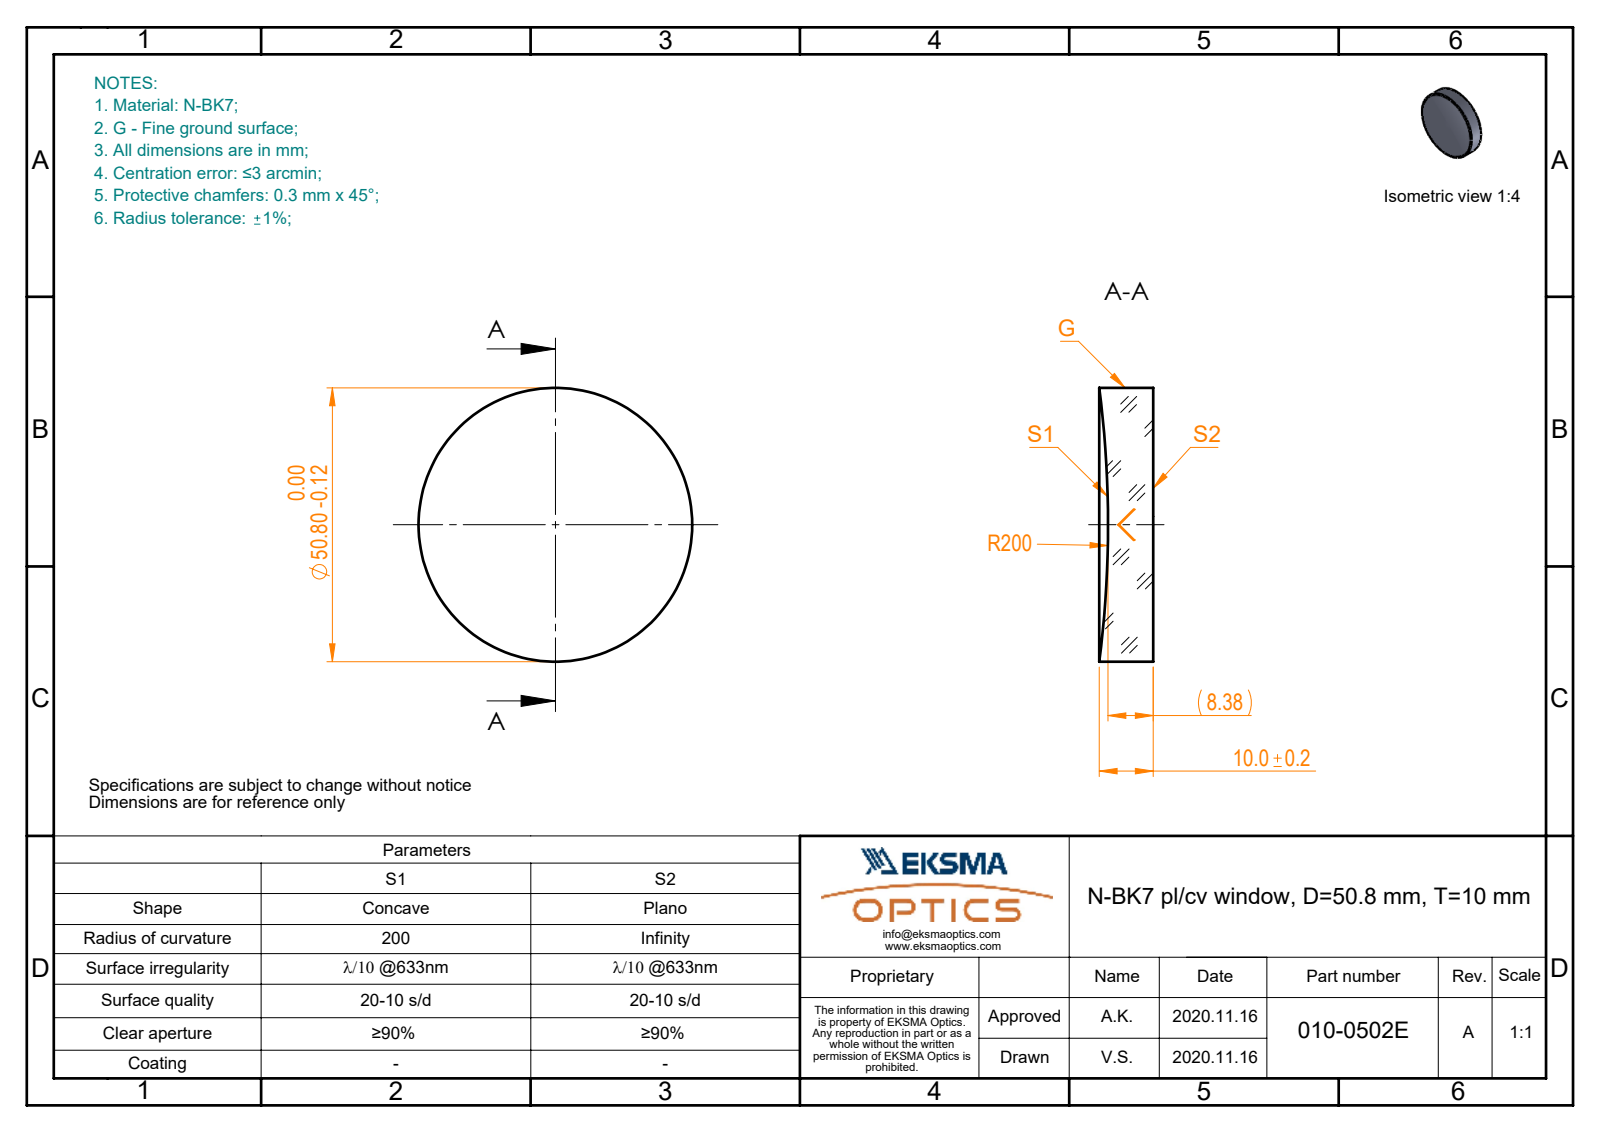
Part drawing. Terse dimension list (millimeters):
name: 010-0502E_N-BK7_PCV_window
written by: SolidWorks 2019 (CONFIG_CONTROL_DESIGN)
unit: mm
bodies: 1 solid, 5 faces (1 planar, 2 cylindrical, 2 other)
size: 50.8 × 50.8 × 10
volume: 18 625 mm³; area: 5 658 mm²
bosses: 1× ⌀50.8
